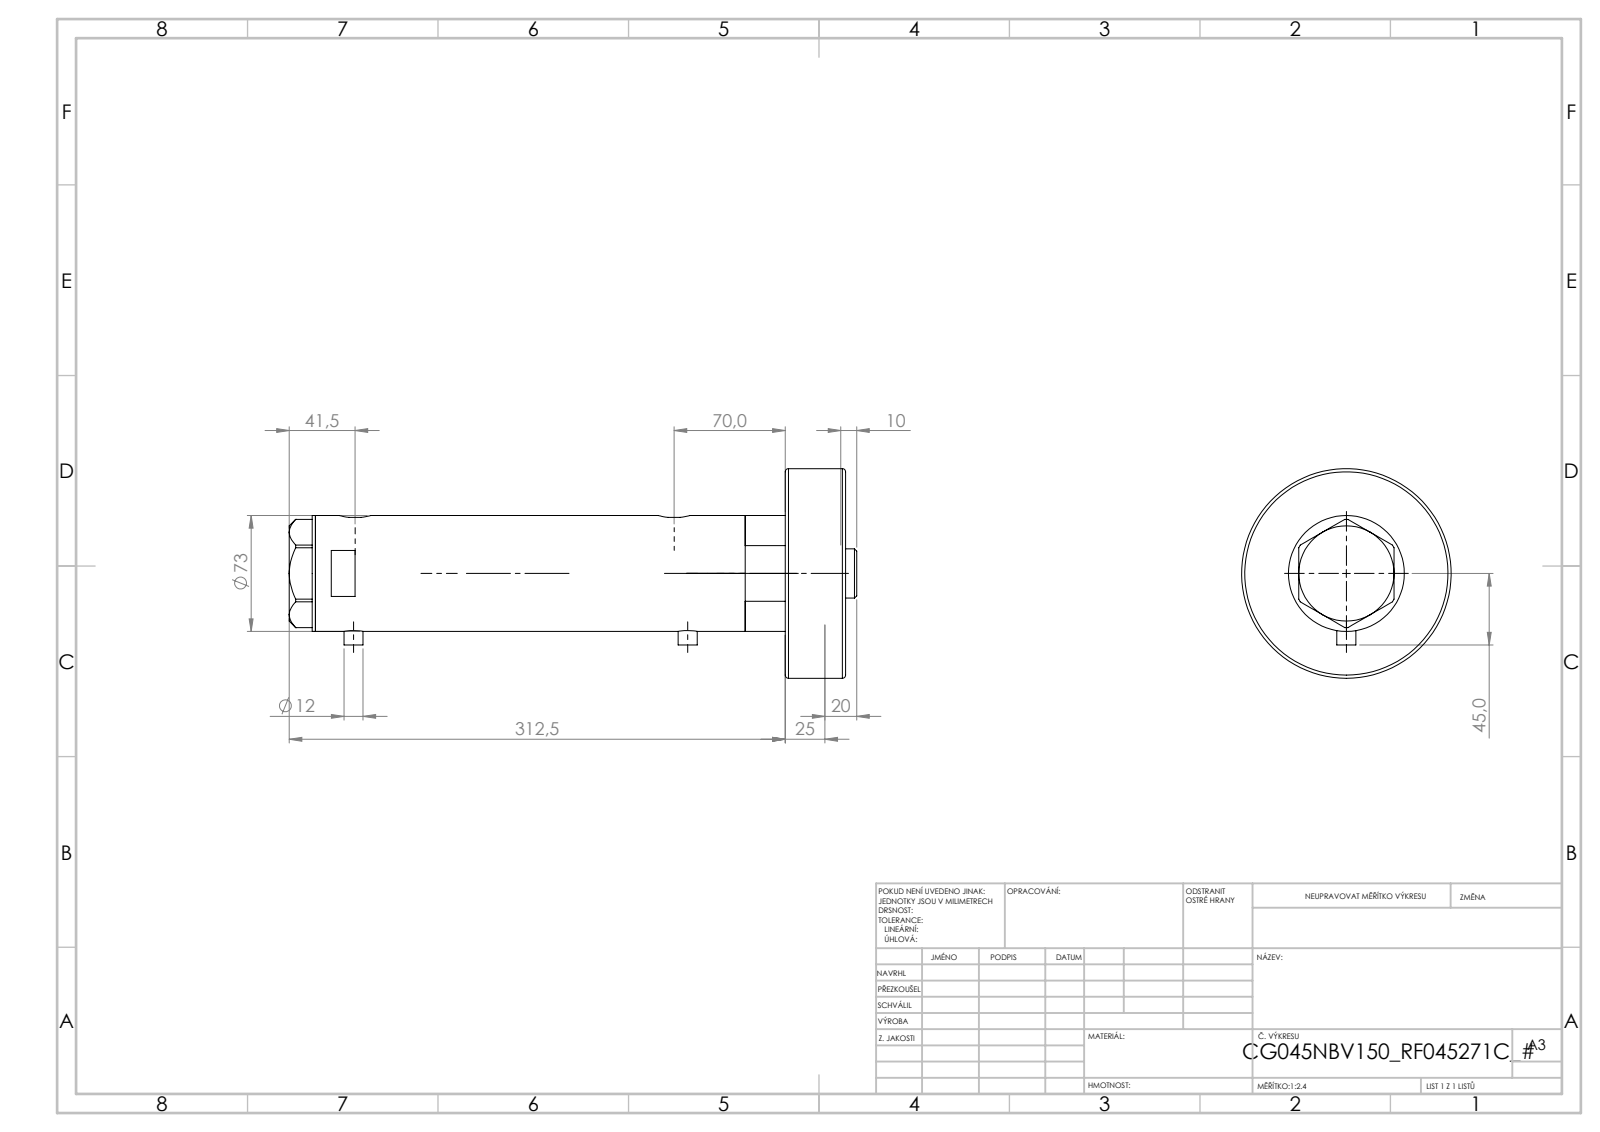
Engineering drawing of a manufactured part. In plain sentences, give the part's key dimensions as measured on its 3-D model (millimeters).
The part is named "V270CG_MIDDLE; V270CG_BACK; V270CG_271C; V270CG_VC (+1 more)". Its 3-D file was written by "SolidWorks 2019 (CONFIG_CONTROL_DESIGN)". It is 5 solids with 130 faces: 51 planar, 55 cylindrical and 24 other. Overall it measures 357.5 by 132 by 132 millimeters. Its volume is 1 659 000 cubic millimeters and its surface area 242 555 square millimeters. Round holes: 2 of diameter 12.5, 2 of diameter 13.16, 1 of diameter 10.5, 1 of diameter 32, 1 of diameter 33.5, 1 of diameter 45, 1 of diameter 48, 1 of diameter 60, 1 of diameter 64. Round bosses or shafts: 2 of diameter 12, 1 of diameter 132, 1 of diameter 73, 1 of diameter 58, 1 of diameter 31. Partial cylindrical surfaces (rounded edges, fillets, slot ends): 2 of radius 10. The main face-to-face distances are 38, 296, 334, 226, 70, 108, 26, 200, 270, 308. The hole center spacings are 1, 8.5, 201, 202, 209.5, 210.5.
